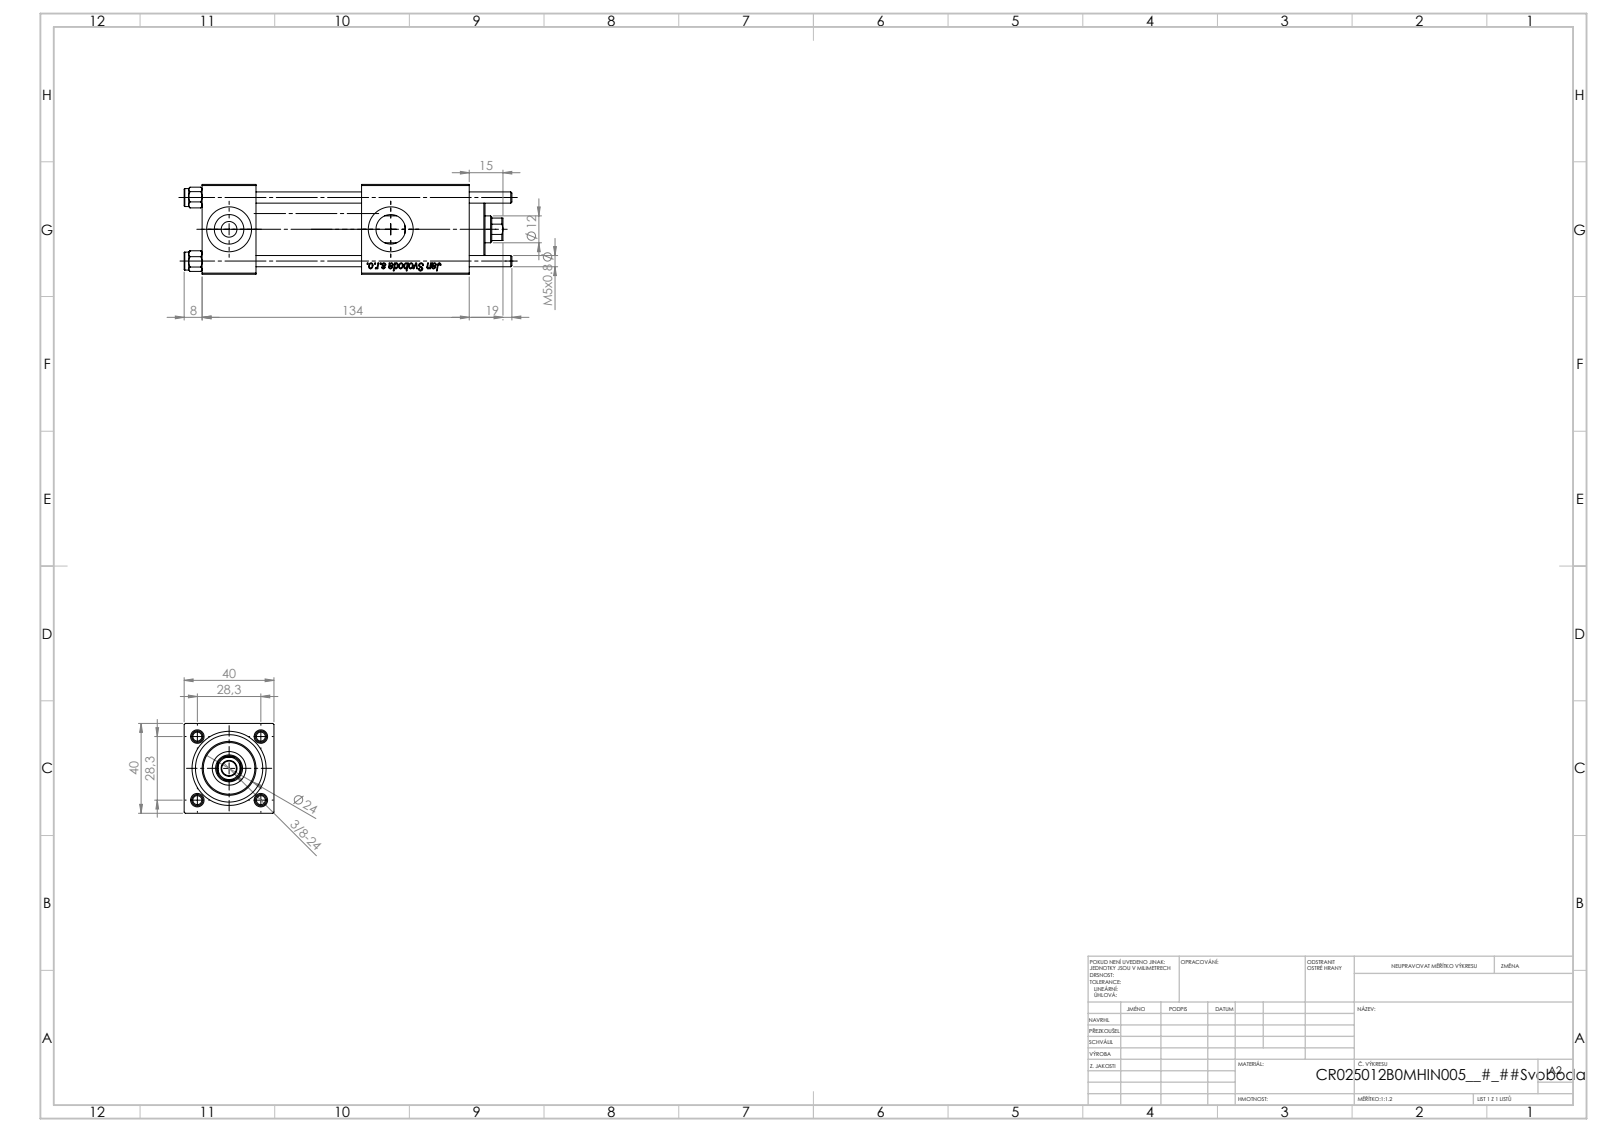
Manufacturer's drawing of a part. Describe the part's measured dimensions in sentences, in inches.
The part is named "V215CR_VCP_B; V215CR_B_TYCINKA; NUT_M5_B; V215_VC_A (+1 more)". Its 3-D file was written by "SolidWorks 2019 (CONFIG_CONTROL_DESIGN)". It is 11 solids with 1155 faces: 429 planar, 78 cylindrical and 648 other. Overall it measures 5.748 by 1.575 by 1.575 inches. Its volume is 8.841 cubic inches and its surface area 90.86 square inches. Round holes: 4 of diameter 0.197, 3 of diameter 0.787, 2 of diameter 0.276, 2 of diameter 0.518, 1 of diameter 0.256, 1 of diameter 0.472, 1 of diameter 0.591, 1 of diameter 0.984, 1 of diameter 1.181. Round bosses or shafts: 4 of diameter 0.315, 1 of diameter 1.22, 1 of diameter 0.945. Partial cylindrical surfaces (rounded edges, fillets, slot ends): 1 of radius 0.217. The main face-to-face distances are 1.575, 0.945, 3.555, 2.61, 2.795, 1.85, 0.76, 4.685, 3.74, 1.89. The hole center spacings are 0.788, 1.114, 1.576, 2.835.
